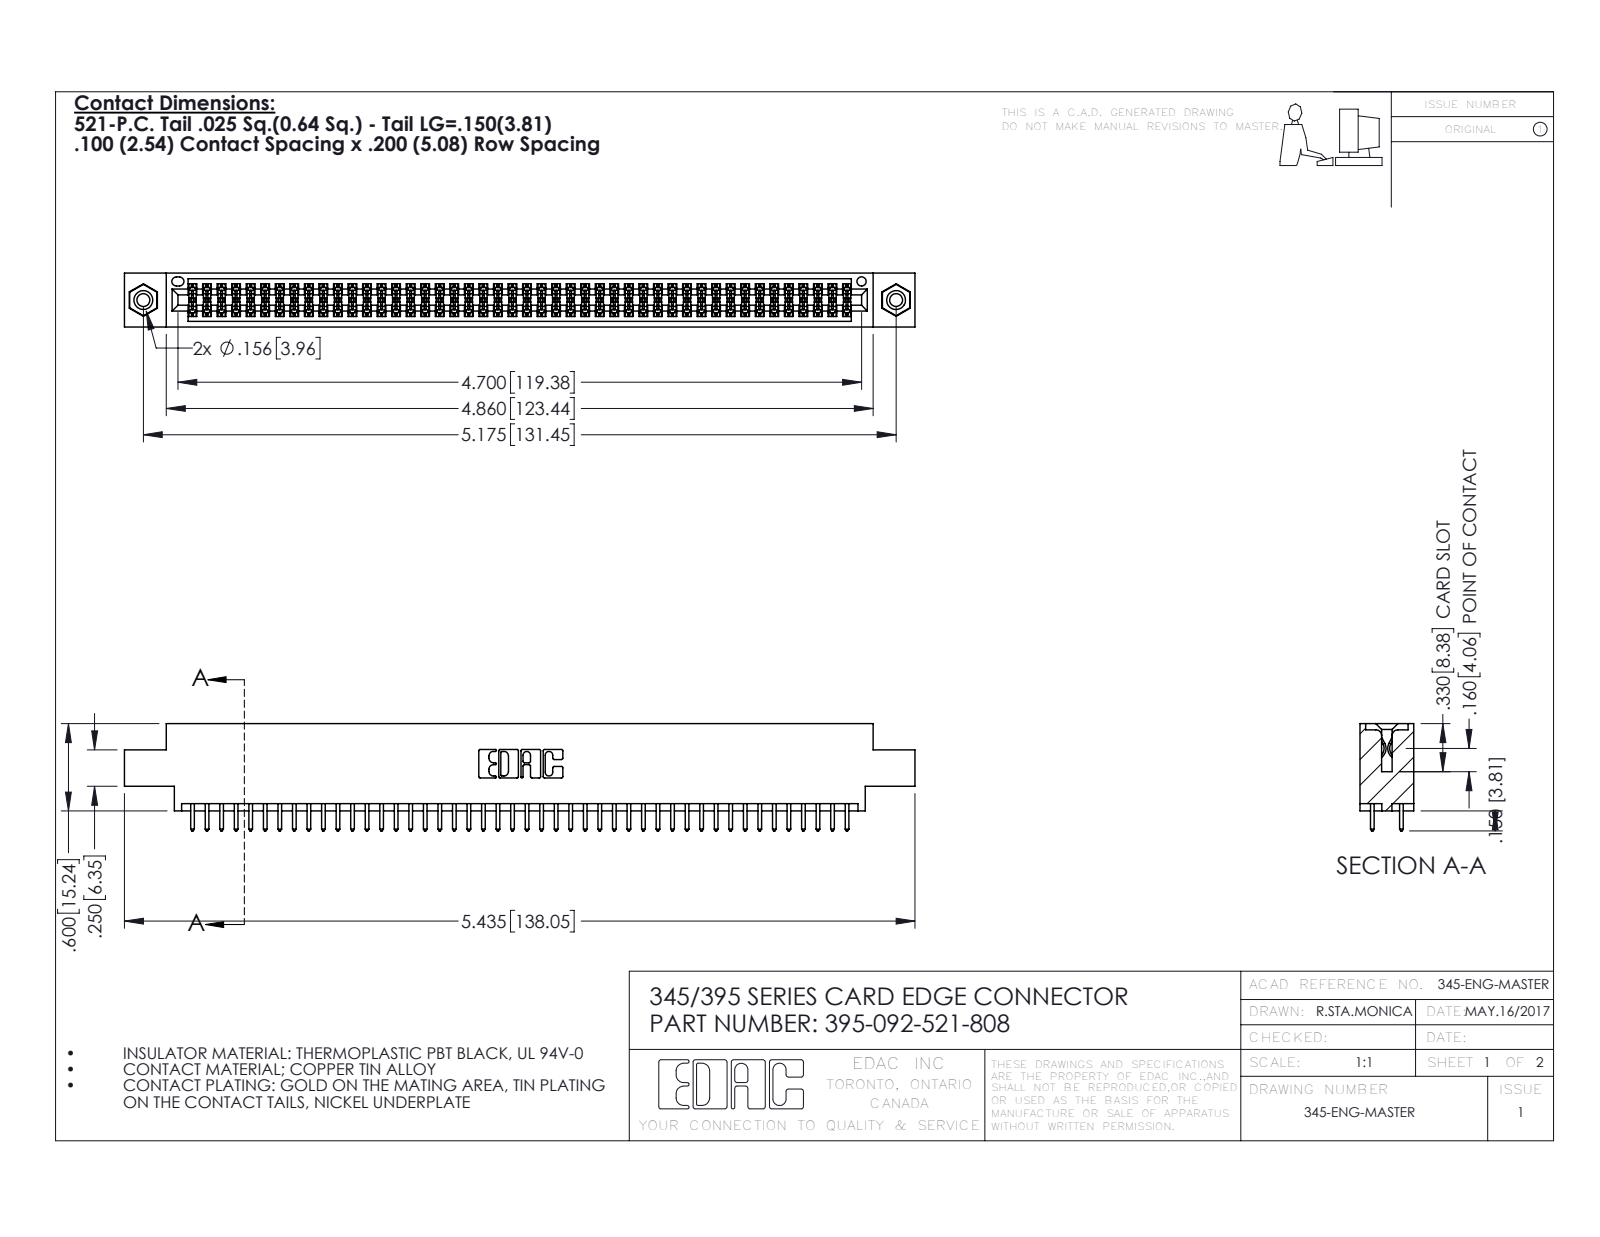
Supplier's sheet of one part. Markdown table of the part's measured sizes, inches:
| quantity | value |
| --- | --- |
| part name | 395-092-521-808; 345 Part_0.170 Offset - 0.156 Dia-TI; 345-292-001_345-293-121; 345-250-001_345-250-003-102 |
| STEP written by | SolidWorks 2016 (CONFIG_CONTROL_DESIGN) |
| units | inches |
| bodies | 95 solids, 4790 faces (3152 planar, 1622 cylindrical, 16 other) |
| overall size | 5.435 × 0.737 × 0.37 |
| volume | 0.811 in³ |
| surface area | 30.43 in² |
| round holes (diameter × count) | 0.089 × 2, 0.125 × 2, 0.156 × 2, 0.064 × 1 |
| round bosses / shafts (diameter × count) | 0.155 × 2 |
| partial cylindrical surfaces (radius × count) | 0.006 × 138, 0.01 × 92, 0.01 × 22, 0.007 × 6, 0.031 × 6, 0.026 × 3, 0.014 × 2, 0.019 × 2 |
| main face-to-face distances | 0.072, 0.298, 0.2, 0.37, 0.098, 0.272, 0.025, 0.225, 0.175, 0.149 |
| hole center spacings | 0.27, 4.939, 5.175 |
